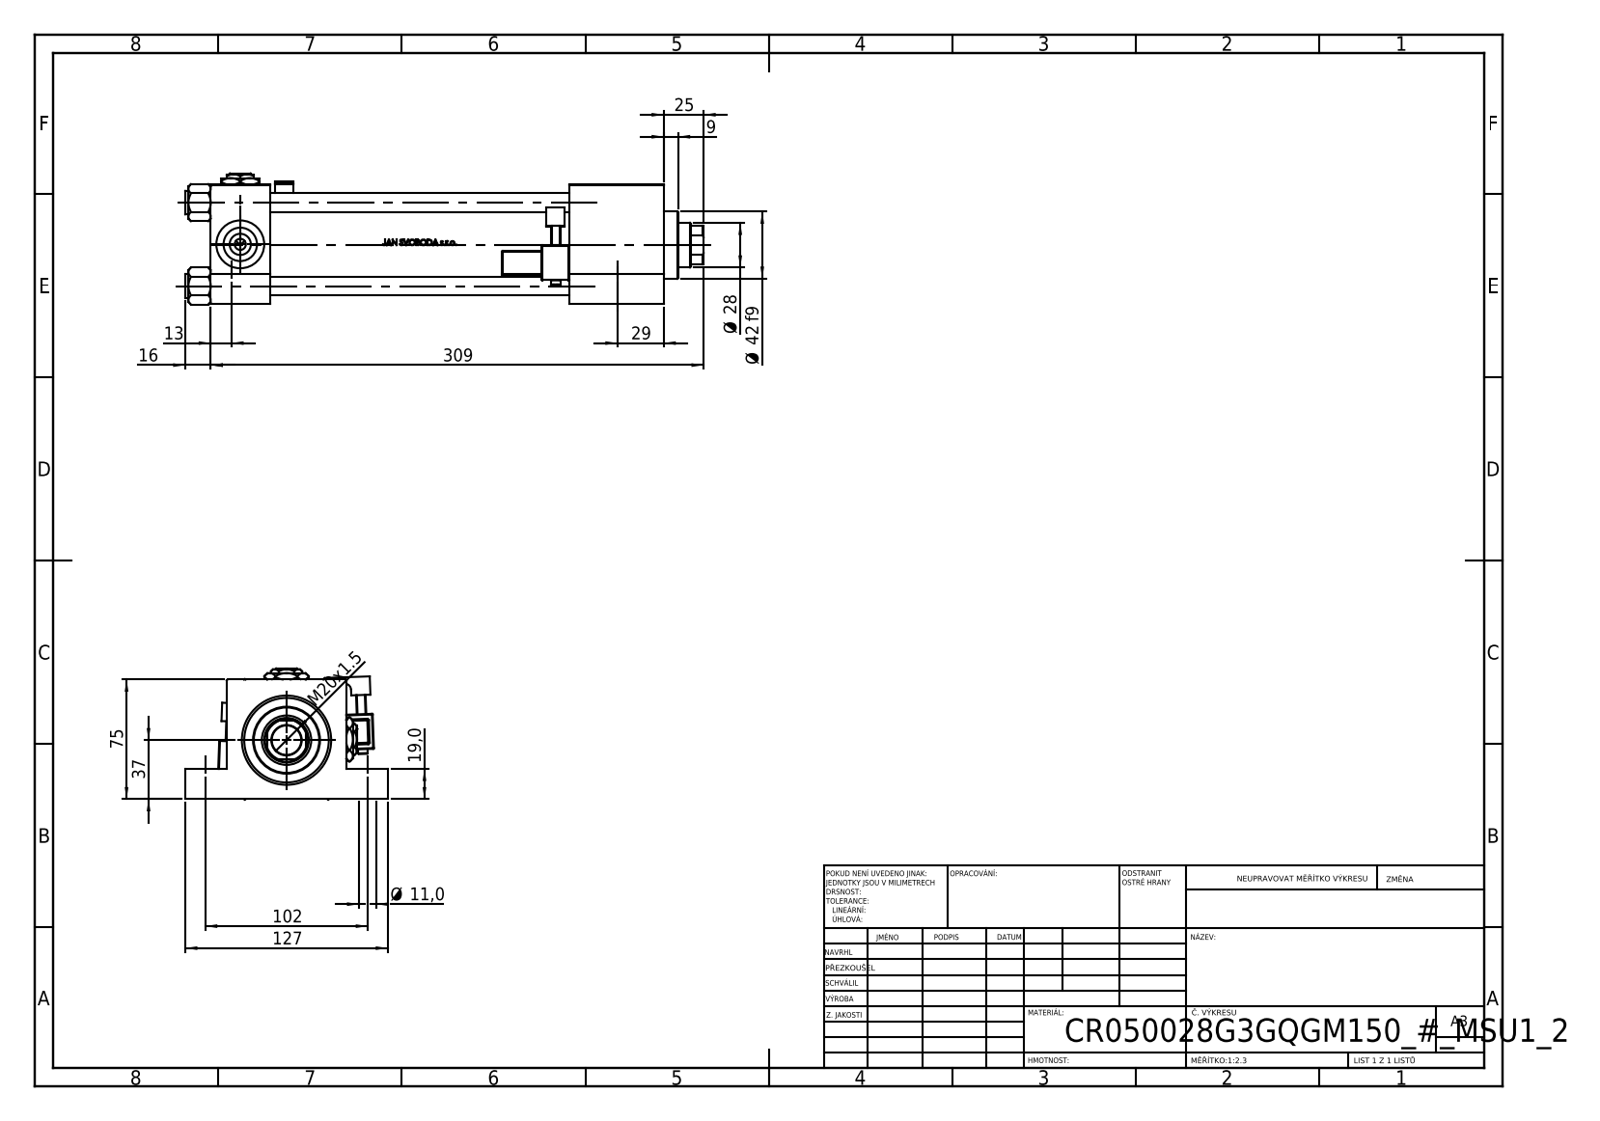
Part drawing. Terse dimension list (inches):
name: V215CR_VCP_G; V215CR_G_TYCINKA; V215CR_MSU; V215CR_G_Body (+3 more)
written by: SolidWorks 2019 (CONFIG_CONTROL_DESIGN)
unit: in
bodies: 15 solids, 1335 faces (535 planar, 190 cylindrical, 610 other)
size: 12.795 × 5 × 3.239
volume: 61.88 in³; area: 393.1 in²
holes: 4× ⌀0.433, 4× ⌀0.472, 3× ⌀0.276, 3× ⌀0.825, 3× ⌀1.181, 1× ⌀0.728, 1× ⌀1.102, 1× ⌀1.22, 1× ⌀1.614, 1× ⌀1.969, 1× ⌀2.087
bosses: 4× ⌀0.591, 2× ⌀0.236, 1× ⌀2.205, 1× ⌀1.654
rounds: 48× R0.02, 2× R0.039, 2× R0.098, 2× R0.157, 1× R0.236, 1× R0.531
face distances: 2.953, 1.457, 11.181, 9.724, 2.205, 8.858, 7.402, 2.323, 0.748, 1.024
hole spacings: 2.059, 1.442, 1.47, 2.02, 2.912, 4.016, 9.525, 9.528
